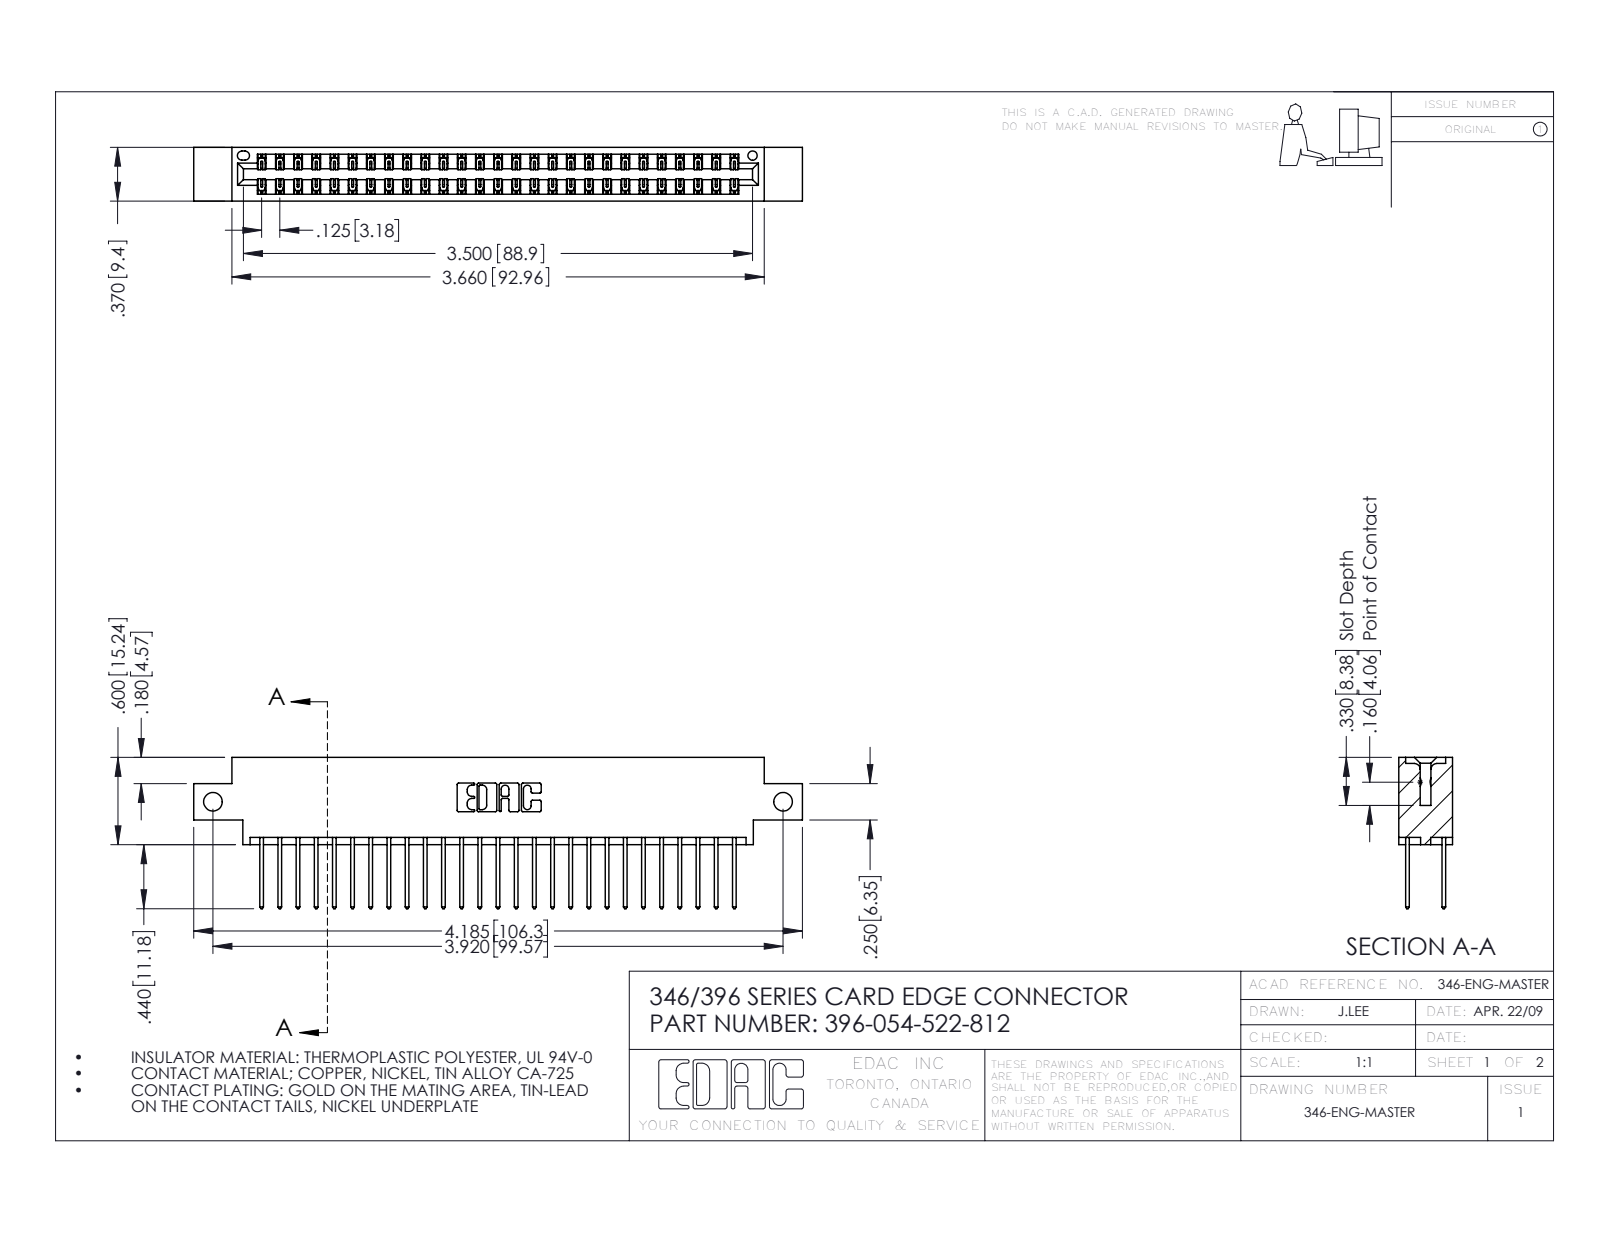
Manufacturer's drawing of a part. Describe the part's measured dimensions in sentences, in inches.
The part is named "345-292-001_345-293-122; 396-054-522-812; 346 Part_0.170 Offset - Side Mount". Its 3-D file was written by "SolidWorks 2016 (CONFIG_CONTROL_DESIGN)". It is 55 solids with 2934 faces: 1970 planar, 964 cylindrical and 0 other. Overall it measures 4.185 by 1.04 by 0.37 inches. Its volume is 0.619 cubic inches and its surface area 22.31 square inches. Round holes: 2 of diameter 0.128, 1 of diameter 0.064. Partial cylindrical surfaces (rounded edges, fillets, slot ends): 81 of radius 0.006, 54 of radius 0.01, 22 of radius 0.01, 6 of radius 0.007, 6 of radius 0.031, 3 of radius 0.026, 2 of radius 0.014, 2 of radius 0.022. The main face-to-face distances are 0.048, 0.322, 0.25, 0.37, 0.072, 0.298, 0.025, 0.275, 0.148, 0.222. The hole center spacings are 3.92.
